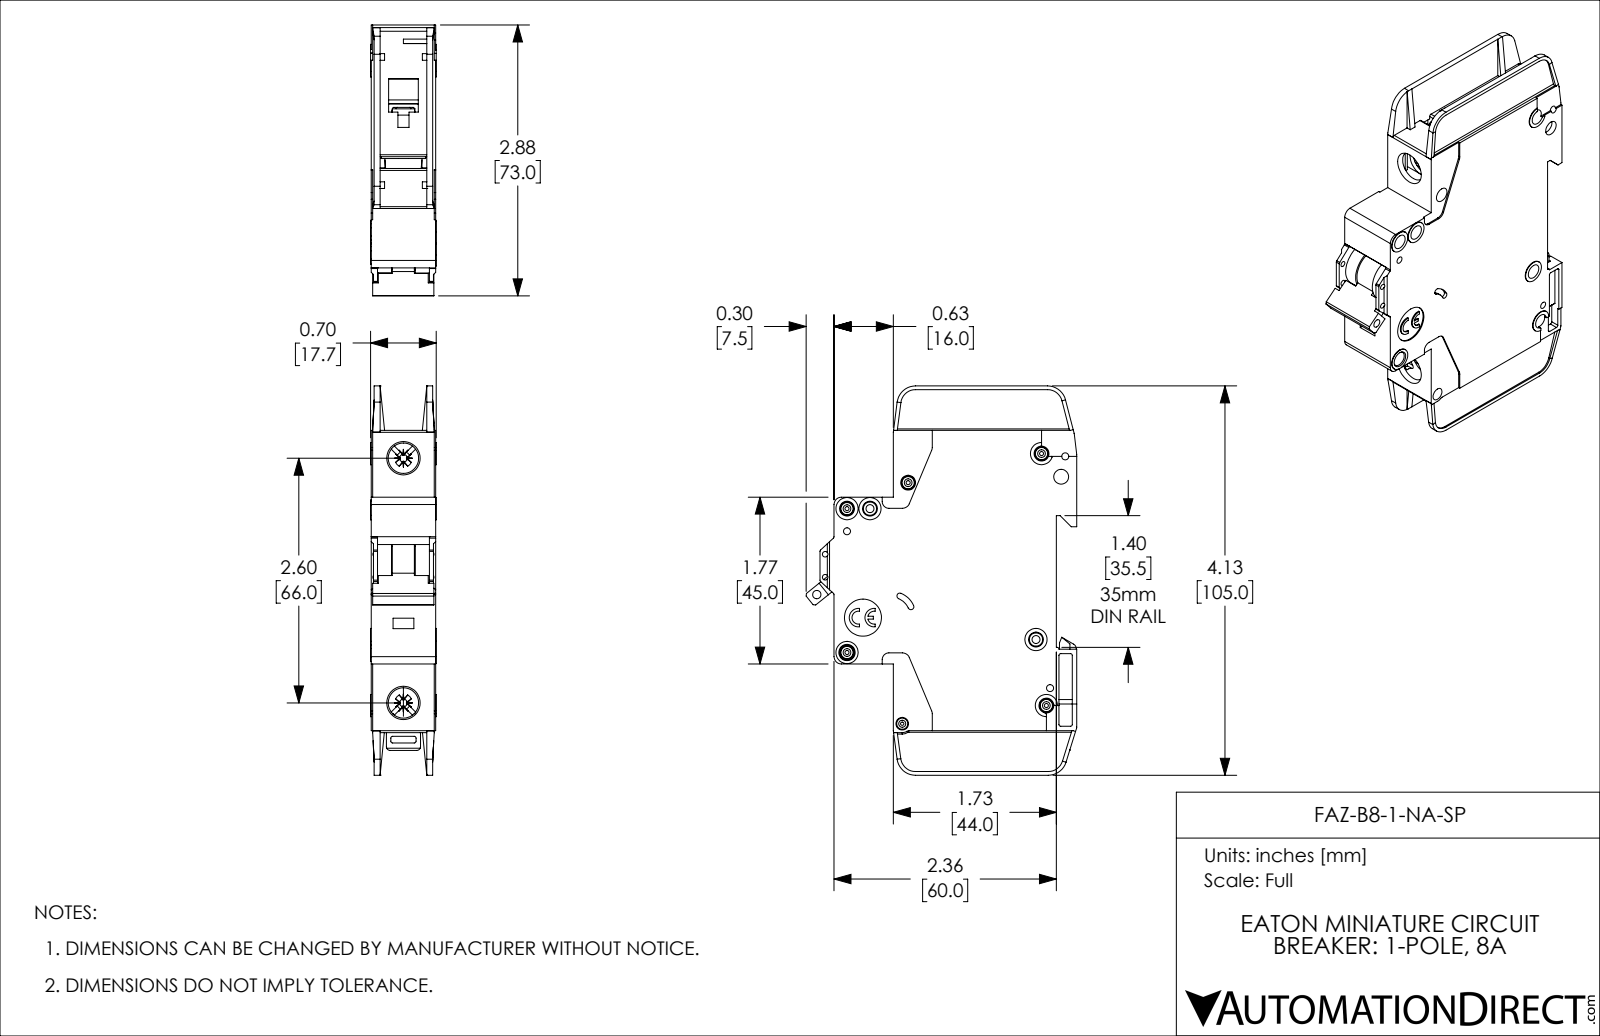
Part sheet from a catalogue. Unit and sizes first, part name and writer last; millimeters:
Units: millimetres
Overall size (bounding box): 105 × 73.1 × 17.7
Round holes (diameter × count): ⌀4 ×8, ⌀1.1 ×5, ⌀1.9 ×4, ⌀1.5 ×2, ⌀2.2 ×2, ⌀8.2 ×2, ⌀0.9 ×1, ⌀2.3 ×1, ⌀2.5 ×1, ⌀3.4 ×1, ⌀10 ×1
Round bosses / shafts (diameter × count): ⌀3.3 ×5, ⌀6 ×4, ⌀3 ×2, ⌀2.5 ×1
Partial cylindrical surfaces — rounded edges, fillets, slot ends (radius × count): R0.5 ×42, R0.4 ×10, R1 ×10, R2 ×8, R5 ×5, R0.2 ×4, R0.7 ×4, R1.1 ×4
Main face-to-face distances: 1.2, 17.4, 15, 16.2, 2.4, 13.8, 0.4, 0.8, 12.6, 14.6
Hole centre spacings: 6.2, 13.6, 22.1, 4.8, 5.1, 5.2, 5.6, 6.1
Volume: 76 720 mm³ · Surface area: 26 460 mm²
Bodies: 1 solid, 1127 faces (671 planar, 357 cylindrical, 99 other)
Part name (STEP PRODUCT): FAZ-B8-1-NA-SP
STEP written by: SolidWorks 2019 (AUTOMOTIVE_DESIGN)
